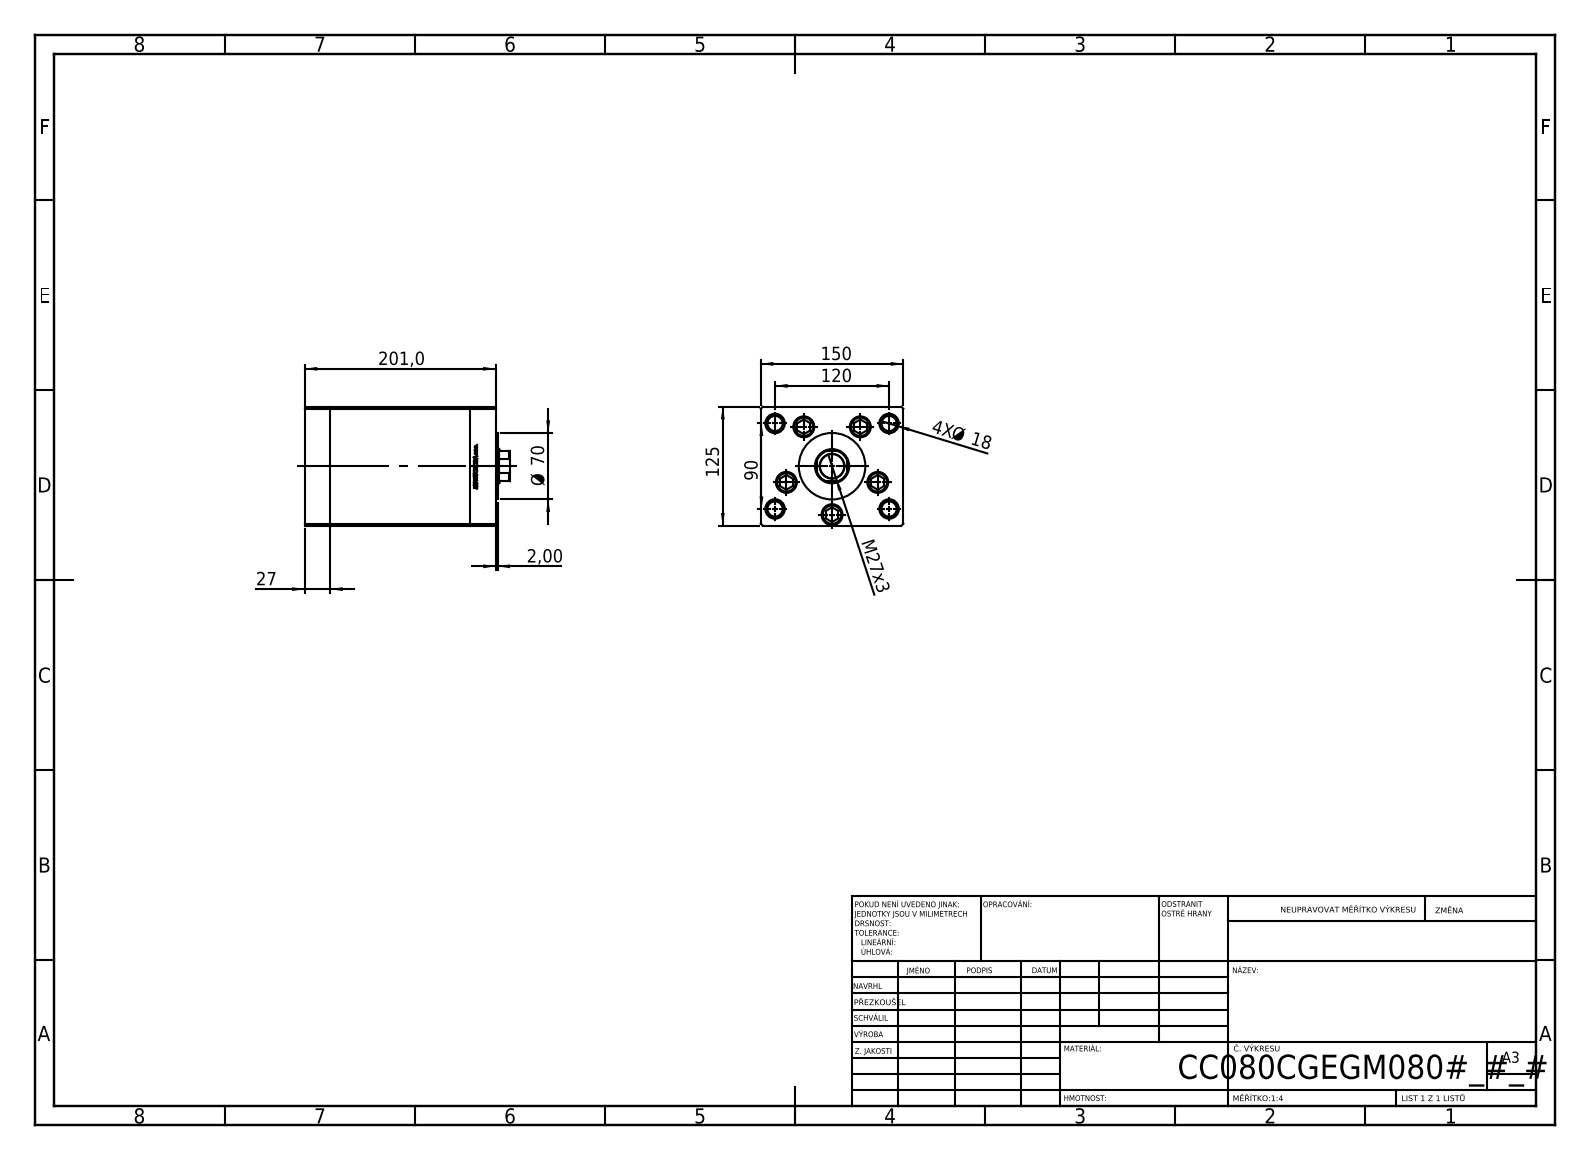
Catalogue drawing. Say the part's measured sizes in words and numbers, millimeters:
The part is named "V220C_C MIDDLE; V220C_VC_C; V220C BACK_C; V220C FRONT (+1 more)". Its 3-D file was written by "SolidWorks 2019 (CONFIG_CONTROL_DESIGN)". It is 13 solids with 1159 faces: 538 planar, 159 cylindrical and 462 other. Overall it measures 216 by 150 by 125 millimeters. Its volume is 3 126 000 cubic millimeters and its surface area 378 820 square millimeters. Round holes: 9 of diameter 17.5, 5 of diameter 22, 4 of diameter 16, 4 of diameter 20.5, 1 of diameter 21, 1 of diameter 25.5, 1 of diameter 36. Round bosses or shafts: 5 of diameter 8, 4 of diameter 21, 1 of diameter 80, 1 of diameter 70. Partial cylindrical surfaces (rounded edges, fillets, slot ends): 2 of radius 0.93, 1 of radius 17.5. The main face-to-face distances are 27, 174, 147, 125, 150, 33.5, 201, 6.5, 167.5, 140.5. The hole center spacings are 51, 75, 30.43, 30.48, 58.89, 60.3, 61.25, 63.14.
